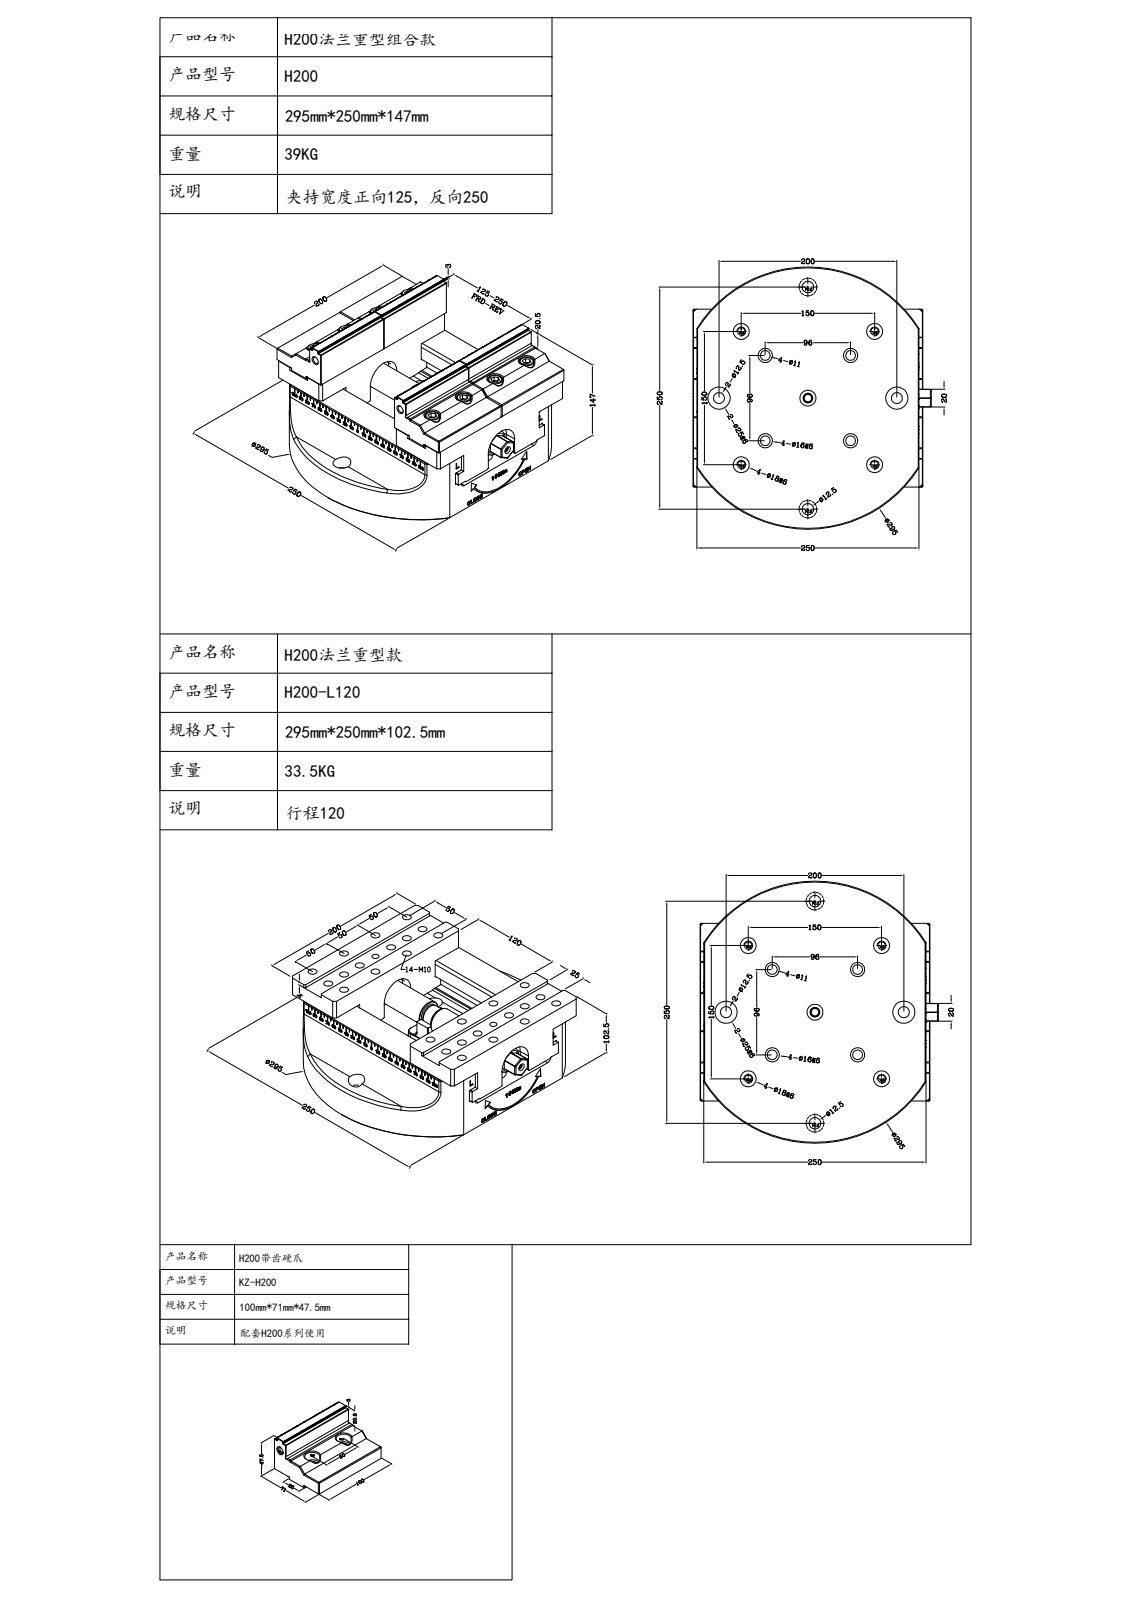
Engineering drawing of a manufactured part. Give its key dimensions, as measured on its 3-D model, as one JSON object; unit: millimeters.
{"part_name": "Admi756Dkqd0", "step_written_by": "SIEMENS PLM Software NX 7.0 (CONFIG_CONTROL_DESIGN)", "units": "millimeters", "bodies": {"solids": 15, "faces": 2728, "planar": 1712, "cylindrical": 399, "other": 617}, "overall_size": [295, 268, 147], "volume_mm3": 4593000, "surface_area_mm2": 490476, "round_holes": [[10, 41], [8.7, 16], [8.5, 9], [11, 9], [18, 9], [8, 7], [12.5, 4], [16, 4], [17, 4], [20, 4], [6.2, 2], [6.7, 2]], "round_bosses_or_shafts": [[16, 8], [29.85, 1], [23.85, 1]], "partial_cylinders_radius": [[1.5, 137], [1, 8], [0.5, 6], [4, 4], [6.75, 4], [6.9, 4], [7.5, 4], [0.25, 2]], "face_to_face_distances": [102.5, 33.75, 68.75, 78, 44.25, 24.5, 187.5, 20.5, 61, 70], "hole_center_spacings": [50, 25, 55.9, 35.36, 79.06, 125.93, 100, 103.08]}
